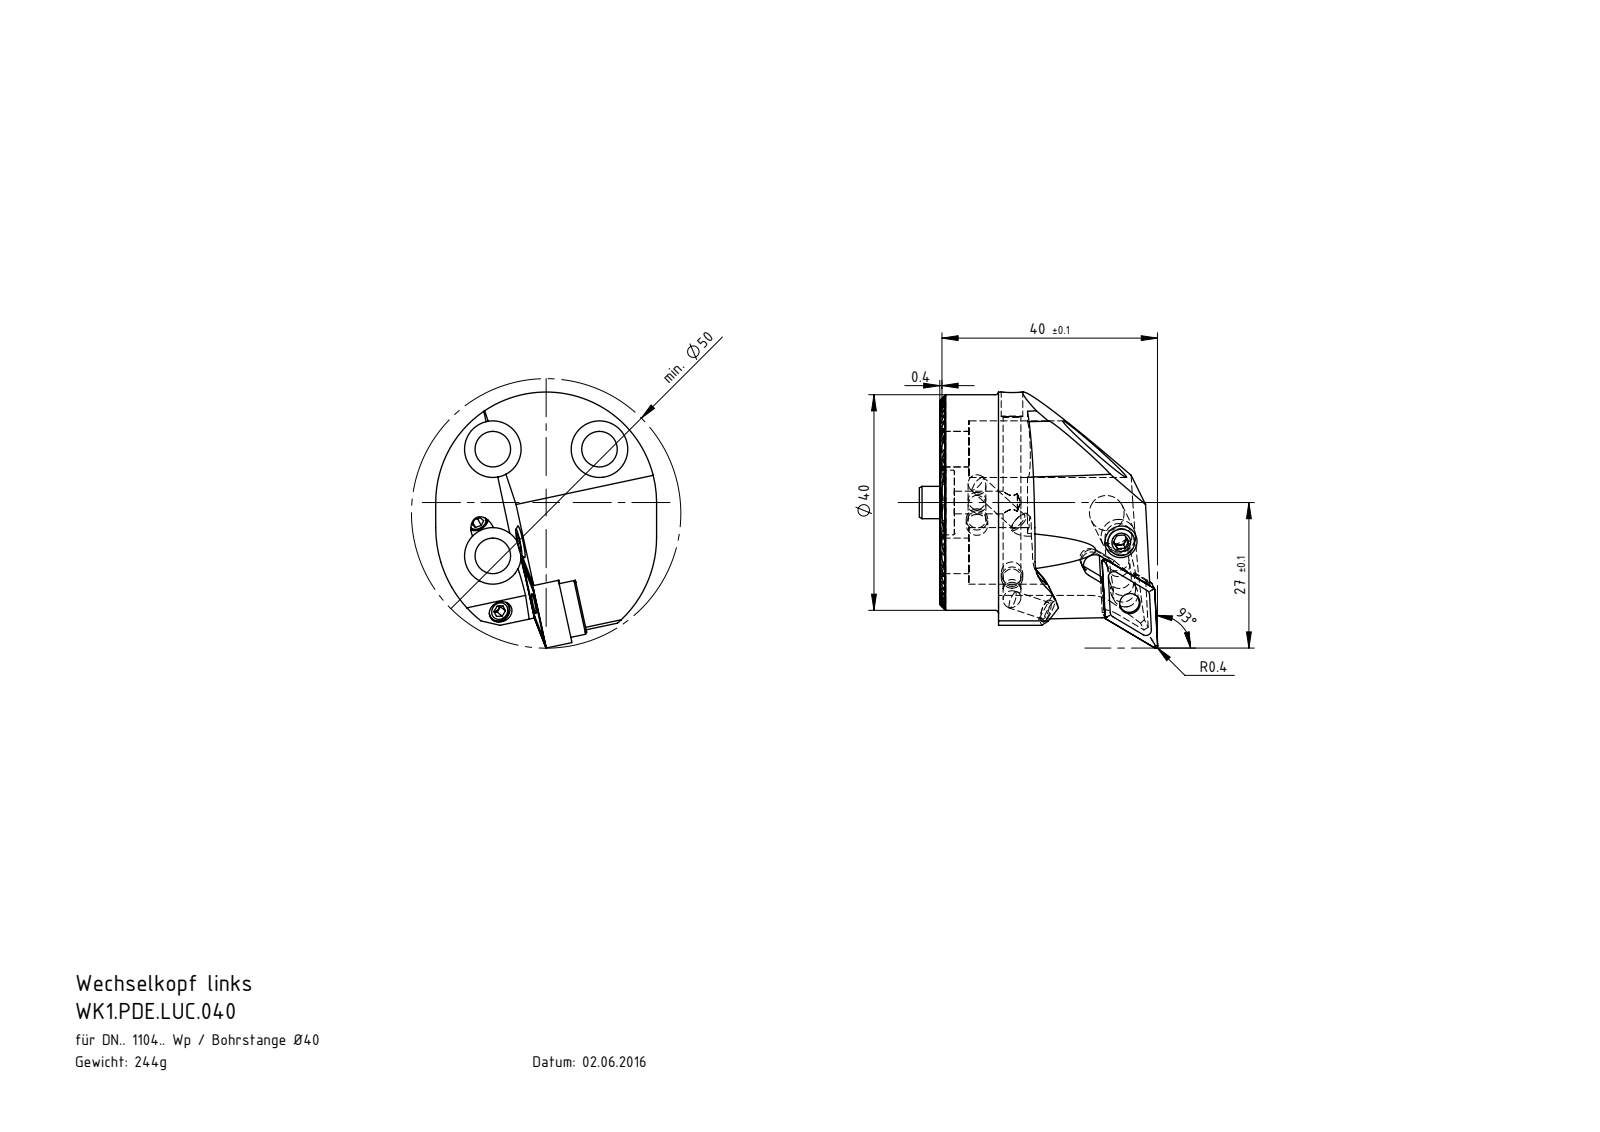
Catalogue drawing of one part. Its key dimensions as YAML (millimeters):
part_name: "KVT_MB_600_040; WDE-ER4.101.017_A; WDE-ER1.101.000; WDE-ER3.101.000_A (+6 more)"
step_written_by: "SolidWorks 2017 (AUTOMOTIVE_DESIGN)"
units: millimeters
bodies: {solids: 15, faces: 506, planar: 277, cylindrical: 119, other: 110}
overall_size: [47.5, 44.25, 41]
volume: 31490
surface_area: 13846
round_holes:
  - {diameter: 3.3, count: 5}
  - {diameter: 3, count: 3}
  - {diameter: 4.2, count: 3}
  - {diameter: 6.6, count: 3}
  - {diameter: 10.5, count: 3}
  - {diameter: 1.7, count: 2}
  - {diameter: 3.81, count: 1}
  - {diameter: 4, count: 1}
  - {diameter: 4.8, count: 1}
  - {diameter: 5, count: 1}
  - {diameter: 6.4, count: 1}
  - {diameter: 12, count: 1}
round_bosses_or_shafts:
  - {diameter: 4, count: 5}
  - {diameter: 6, count: 2}
  - {diameter: 40, count: 1}
  - {diameter: 5.9, count: 1}
  - {diameter: 2.87, count: 1}
partial_cylinders:
  - {radius: 0.12, count: 26}
  - {radius: 0.4, count: 8}
  - {radius: 2.1, count: 5}
  - {radius: 7, count: 2}
  - {radius: 1.83, count: 1}
  - {radius: 1.85, count: 1}
  - {radius: 2.25, count: 1}
  - {radius: 2.35, count: 1}
face_to_face_distances: [1.3, 2.6, 3.9, 12.99, 5.2, 11.69, 9.09, 10.39, 7.79, 7.8]
hole_center_spacings: [14, 19.8, 11.81, 28]
